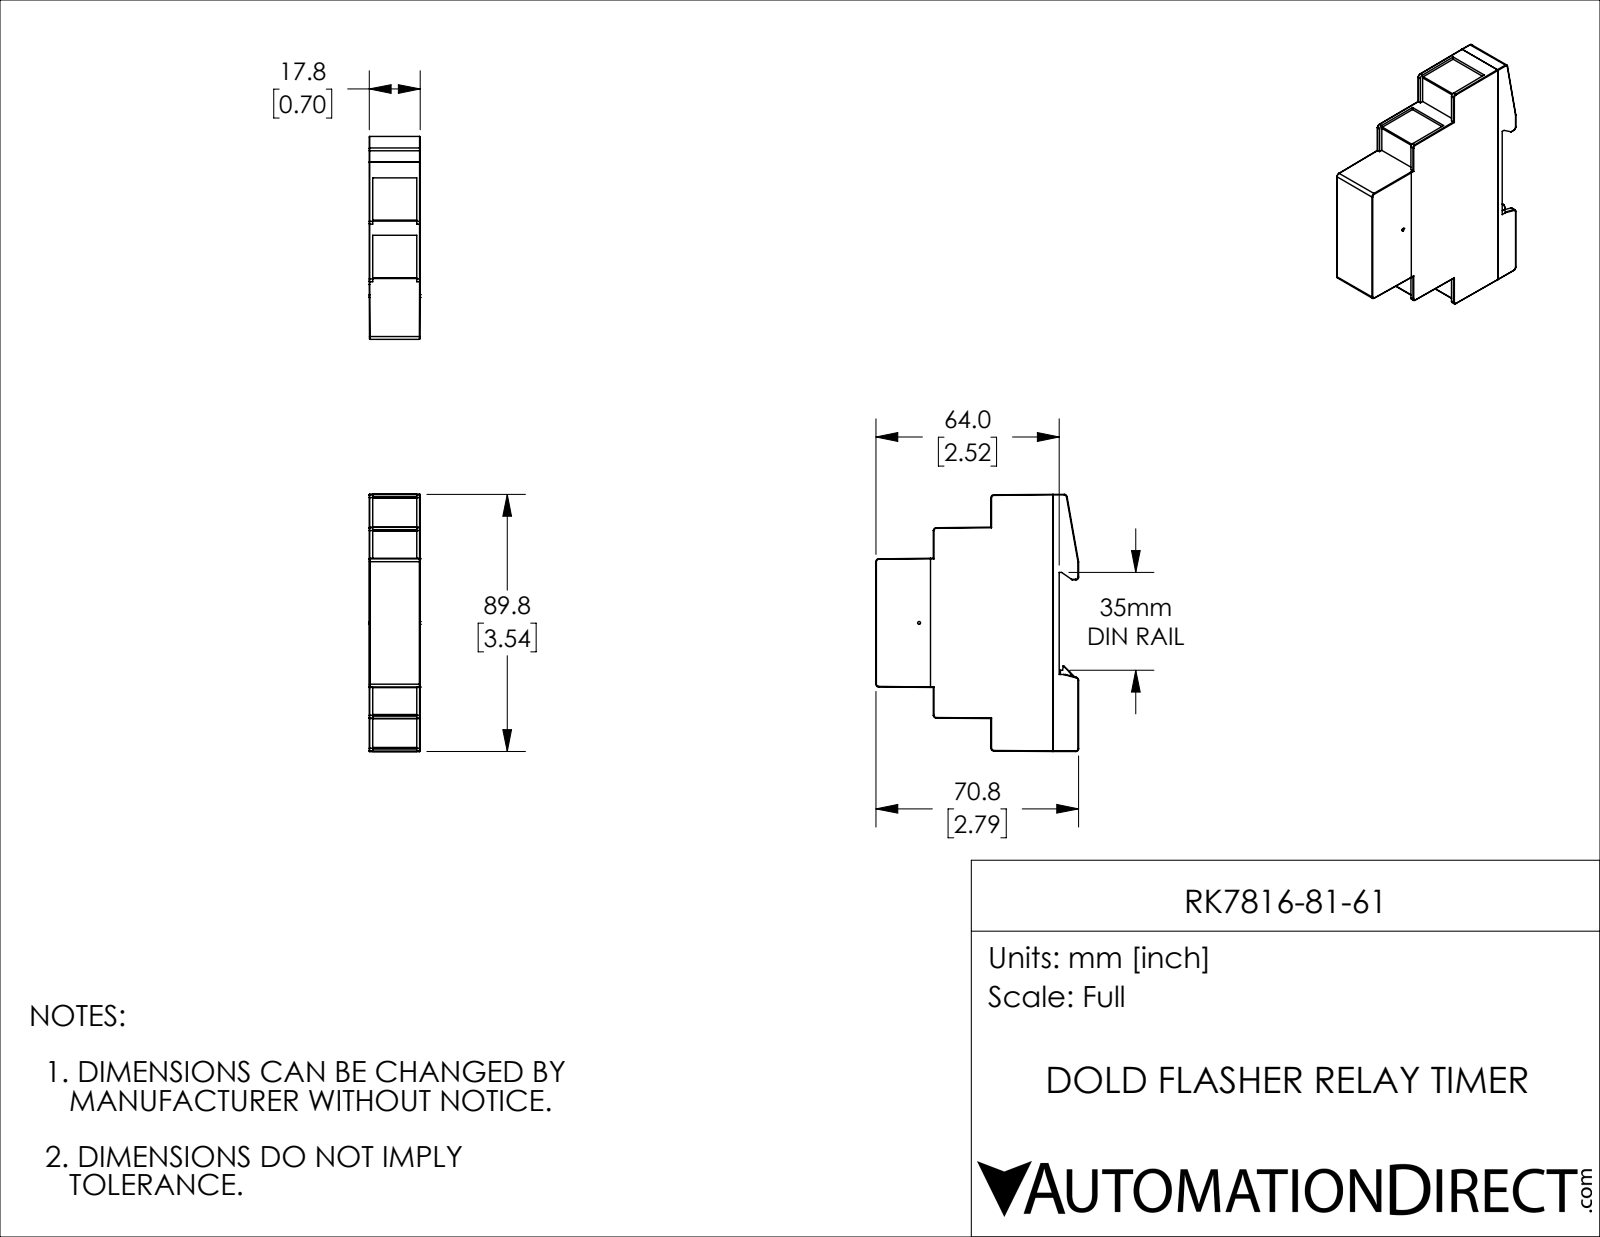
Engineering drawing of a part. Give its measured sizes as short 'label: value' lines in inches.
name: RK7816-81-61
written by: SolidWorks 2019 (CONFIG_CONTROL_DESIGN)
unit: in
bodies: 3 solids, 267 faces (158 planar, 85 cylindrical, 24 other)
size: 3.535 × 2.787 × 0.701
volume: 4.945 in³; area: 31.16 in²
bosses: 1× ⌀0.039
rounds: 36× R0.008, 12× R0.039, 9× R0.004, 4× R0.012, 2× R0.02, 1× R0.011, 1× R0.031, 1× R0.118
face distances: 0.701, 0.085, 2.52, 2.435, 0.383, 0.446, 0.829, 0.791, 0.835, 0.894
